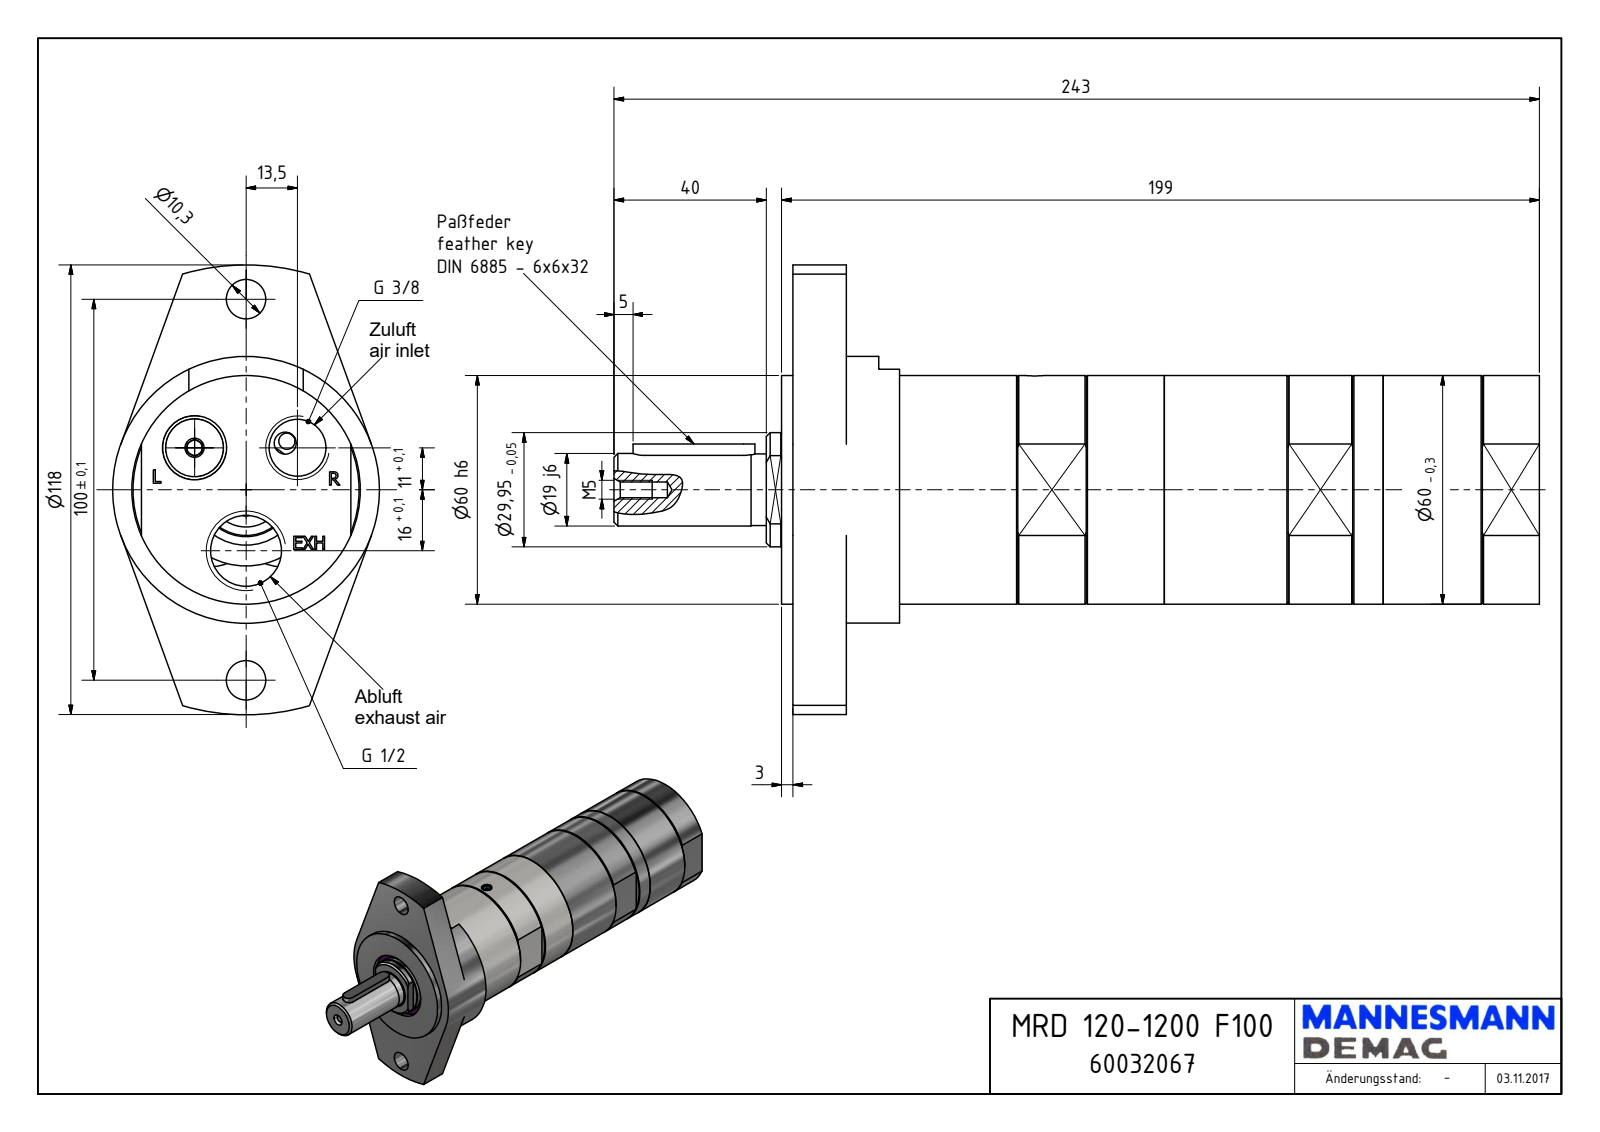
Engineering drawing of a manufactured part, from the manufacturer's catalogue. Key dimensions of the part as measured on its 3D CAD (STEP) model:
Part name (STEP PRODUCT): MRD 120-1200 F100_60032067
STEP written by: Autodesk Inventor 2018 (AUTOMOTIVE_DESIGN)
Units: millimetres
Bodies: 1 solid, 518 faces (227 planar, 246 cylindrical, 45 other)
Overall size (bounding box): 243 × 118 × 70
Volume: 617 583 mm³ · Surface area: 66 197 mm²
Round holes (diameter × count): ⌀4 ×2, ⌀10.3 ×2, ⌀14.95 ×2, ⌀1.55 ×1, ⌀4.13 ×1, ⌀5.5 ×1, ⌀18.63 ×1, ⌀35 ×1, ⌀53.38 ×1, ⌀57.01 ×1
Round bosses / shafts (diameter × count): ⌀70 ×1, ⌀60 ×1, ⌀57 ×1, ⌀56.86 ×1, ⌀55.18 ×1, ⌀53.18 ×1, ⌀29.95 ×1, ⌀19 ×1
Partial cylindrical surfaces — rounded edges, fillets, slot ends (radius × count): R11.68 ×94, R3 ×2, R7.5 ×2, R8.5 ×1, R19.41 ×1, R23.5 ×1, R24.79 ×1, R24.96 ×1
Main face-to-face distances: 14, 196, 182, 3, 17, 199, 55, 28, 31, 168
Hole centre spacings: 17.41, 30.19, 41.27, 50, 62.48, 16, 27, 34
